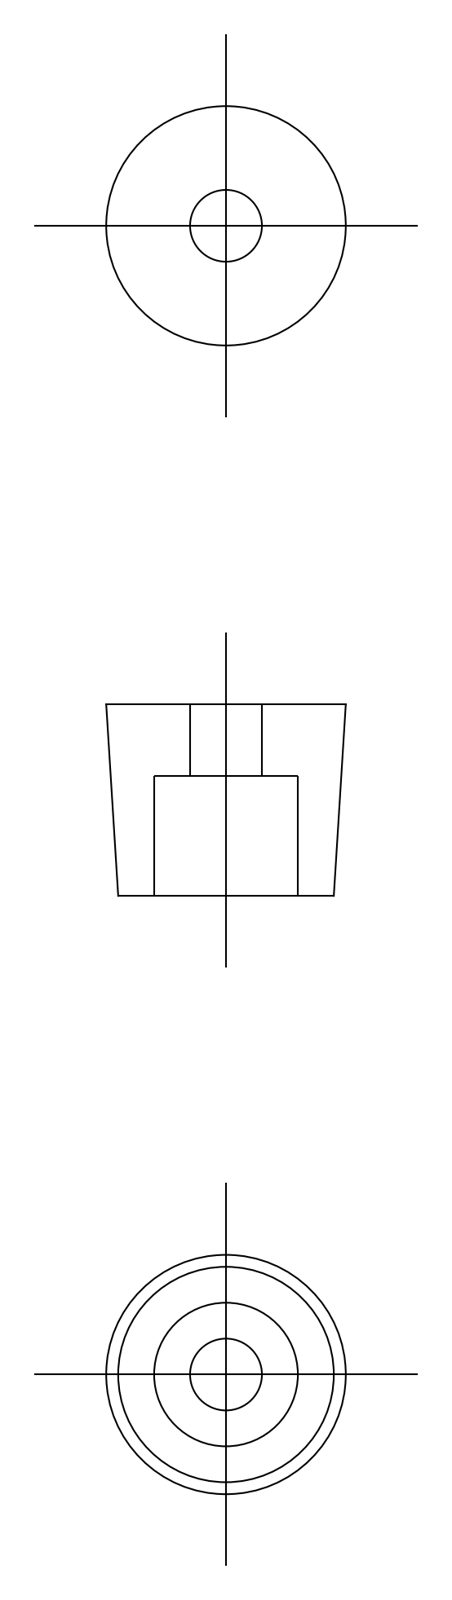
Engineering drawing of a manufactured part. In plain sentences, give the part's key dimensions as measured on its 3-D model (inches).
The part is named "washer; rubber foot; CK_7_1202_36". Its 3-D file was written by "CADfix (AUTOMOTIVE_DESIGN)". It is 2 solids with 21 faces: 0 planar, 0 cylindrical and 21 other. Overall it measures 0.394 by 0.394 by 0.315 inches. Its volume is 0.025 cubic inches and its surface area 1 square inches.
